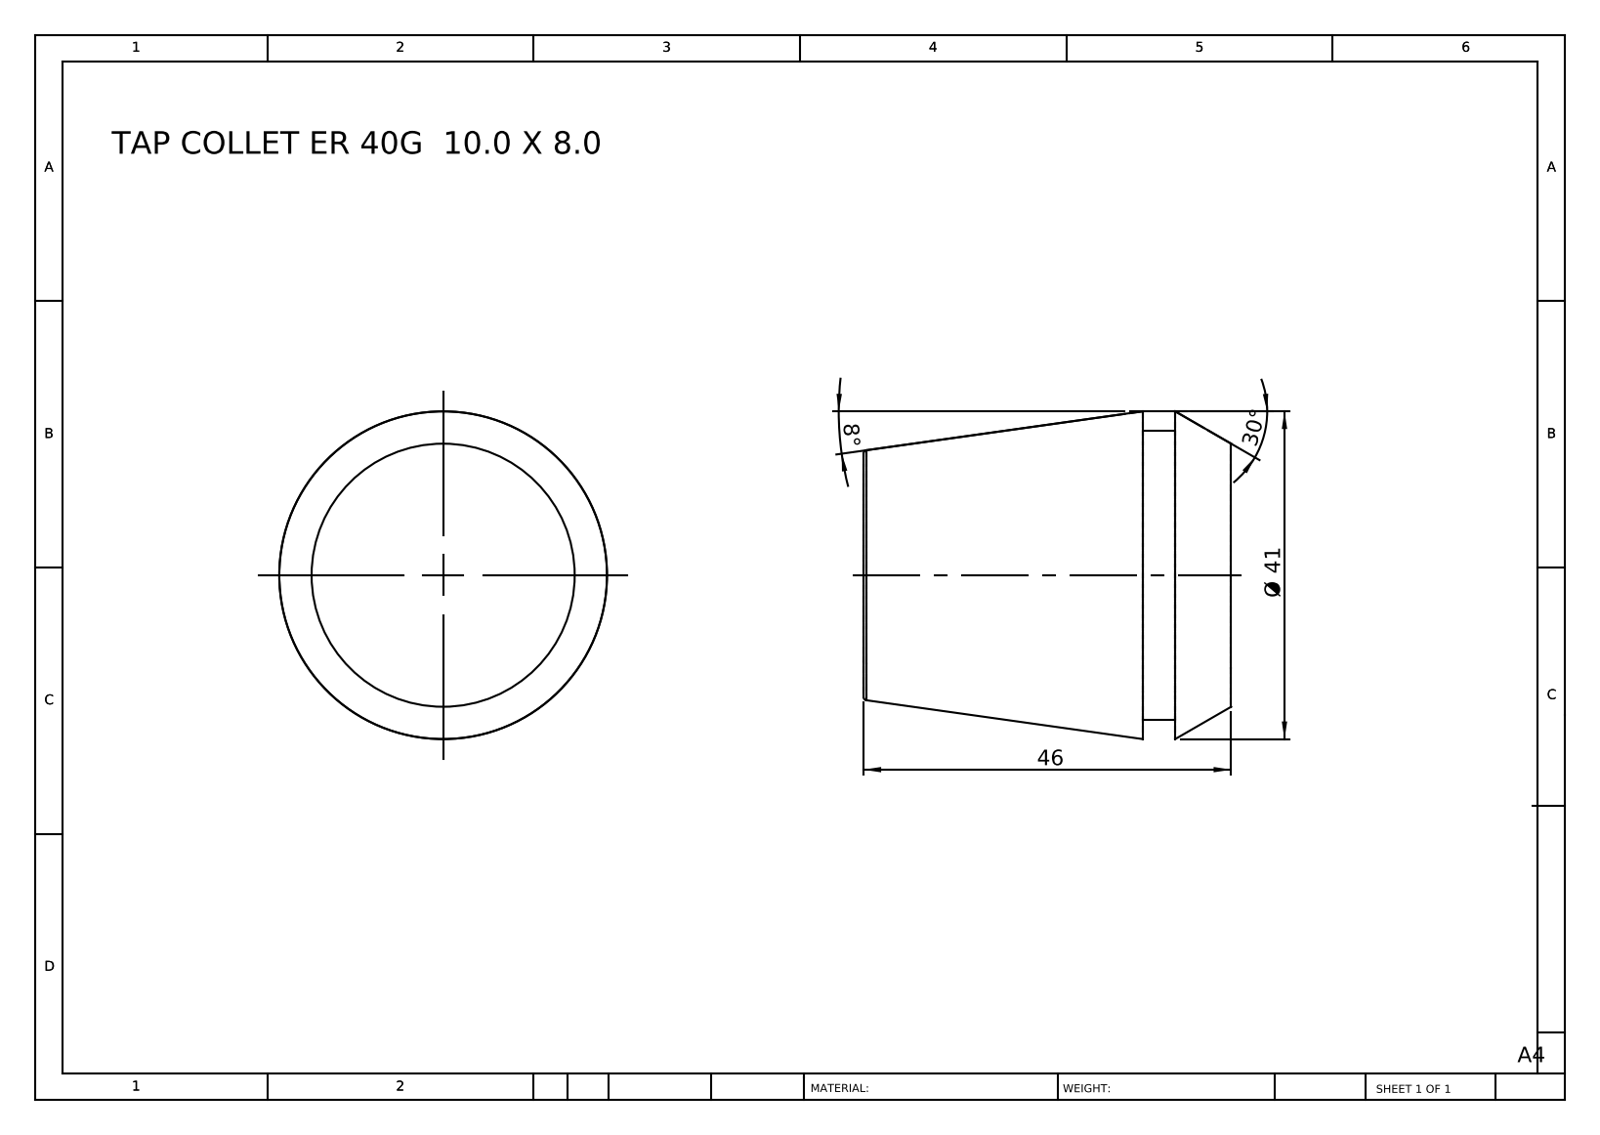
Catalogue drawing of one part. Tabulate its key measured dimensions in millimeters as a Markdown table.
| quantity | value |
| --- | --- |
| part name | TAP COLLET ER 40G 10.0 X 8.0 |
| STEP written by | SolidWorks 2014 (CONFIG_CONTROL_DESIGN) |
| units | millimeters |
| bodies | 1 solid, 12 faces (4 planar, 2 cylindrical, 6 other) |
| overall size | 46 × 41 × 41 |
| volume | 47 690 mm³ |
| surface area | 7 586 mm² |
| round bosses / shafts (diameter × count) | 36.2 × 1 |
| main face-to-face distances | 46, 11.1, 34.9, 7, 4.1, 39 |
